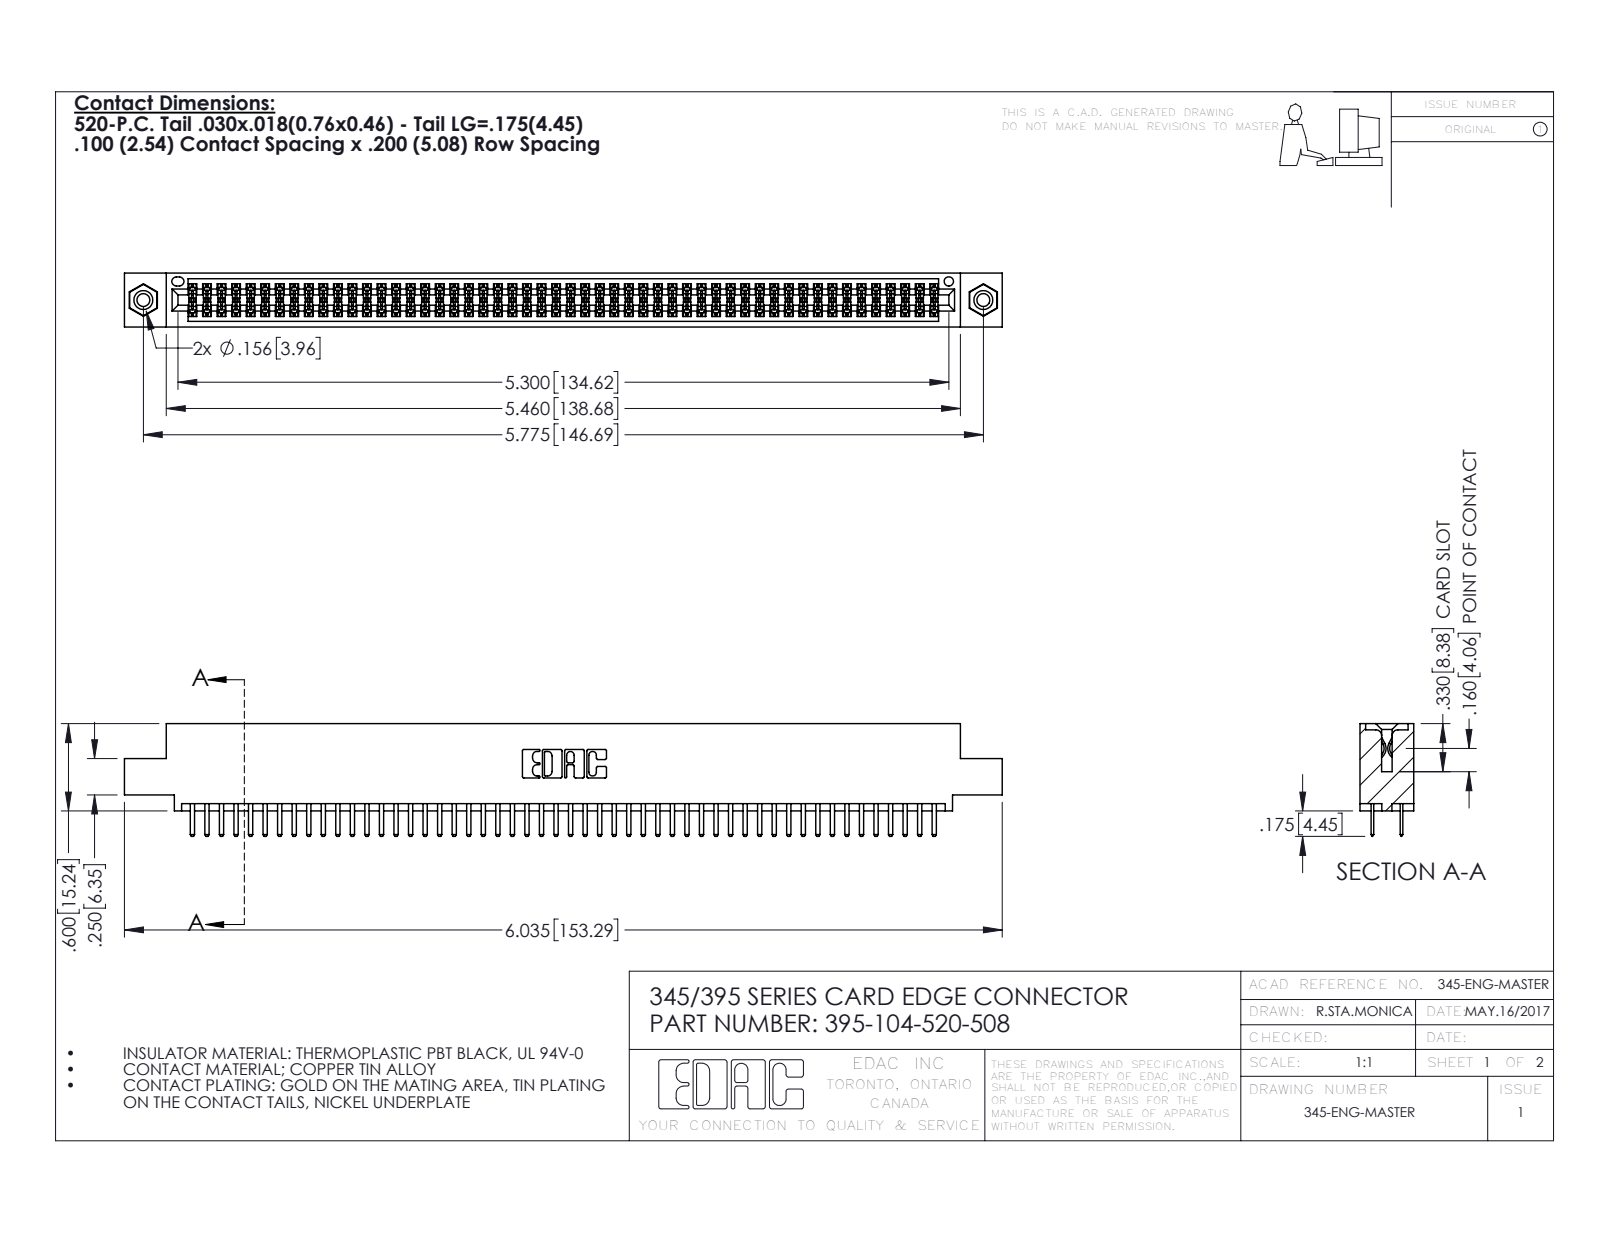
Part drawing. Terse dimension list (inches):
name: 345-250-001_345-250-003-102; 345 Part_0.110 Offset - 0.156 Dia-TI; 345-292-001_345-293-120; 395-104-520-508
written by: SolidWorks 2016 (CONFIG_CONTROL_DESIGN)
unit: in
bodies: 107 solids, 5806 faces (3756 planar, 2034 cylindrical, 16 other)
size: 6.035 × 0.775 × 0.37
volume: 0.907 in³; area: 34.36 in²
holes: 2× ⌀0.089, 2× ⌀0.125, 2× ⌀0.156, 1× ⌀0.064
bosses: 2× ⌀0.155
rounds: 156× R0.006, 108× R0.01, 22× R0.01, 6× R0.007, 6× R0.031, 3× R0.026, 2× R0.014, 2× R0.019
face distances: 0.072, 0.298, 0.2, 0.37, 0.098, 0.272, 0.025, 0.225, 0.022, 0.072
hole spacings: 0.27, 5.539, 5.775
